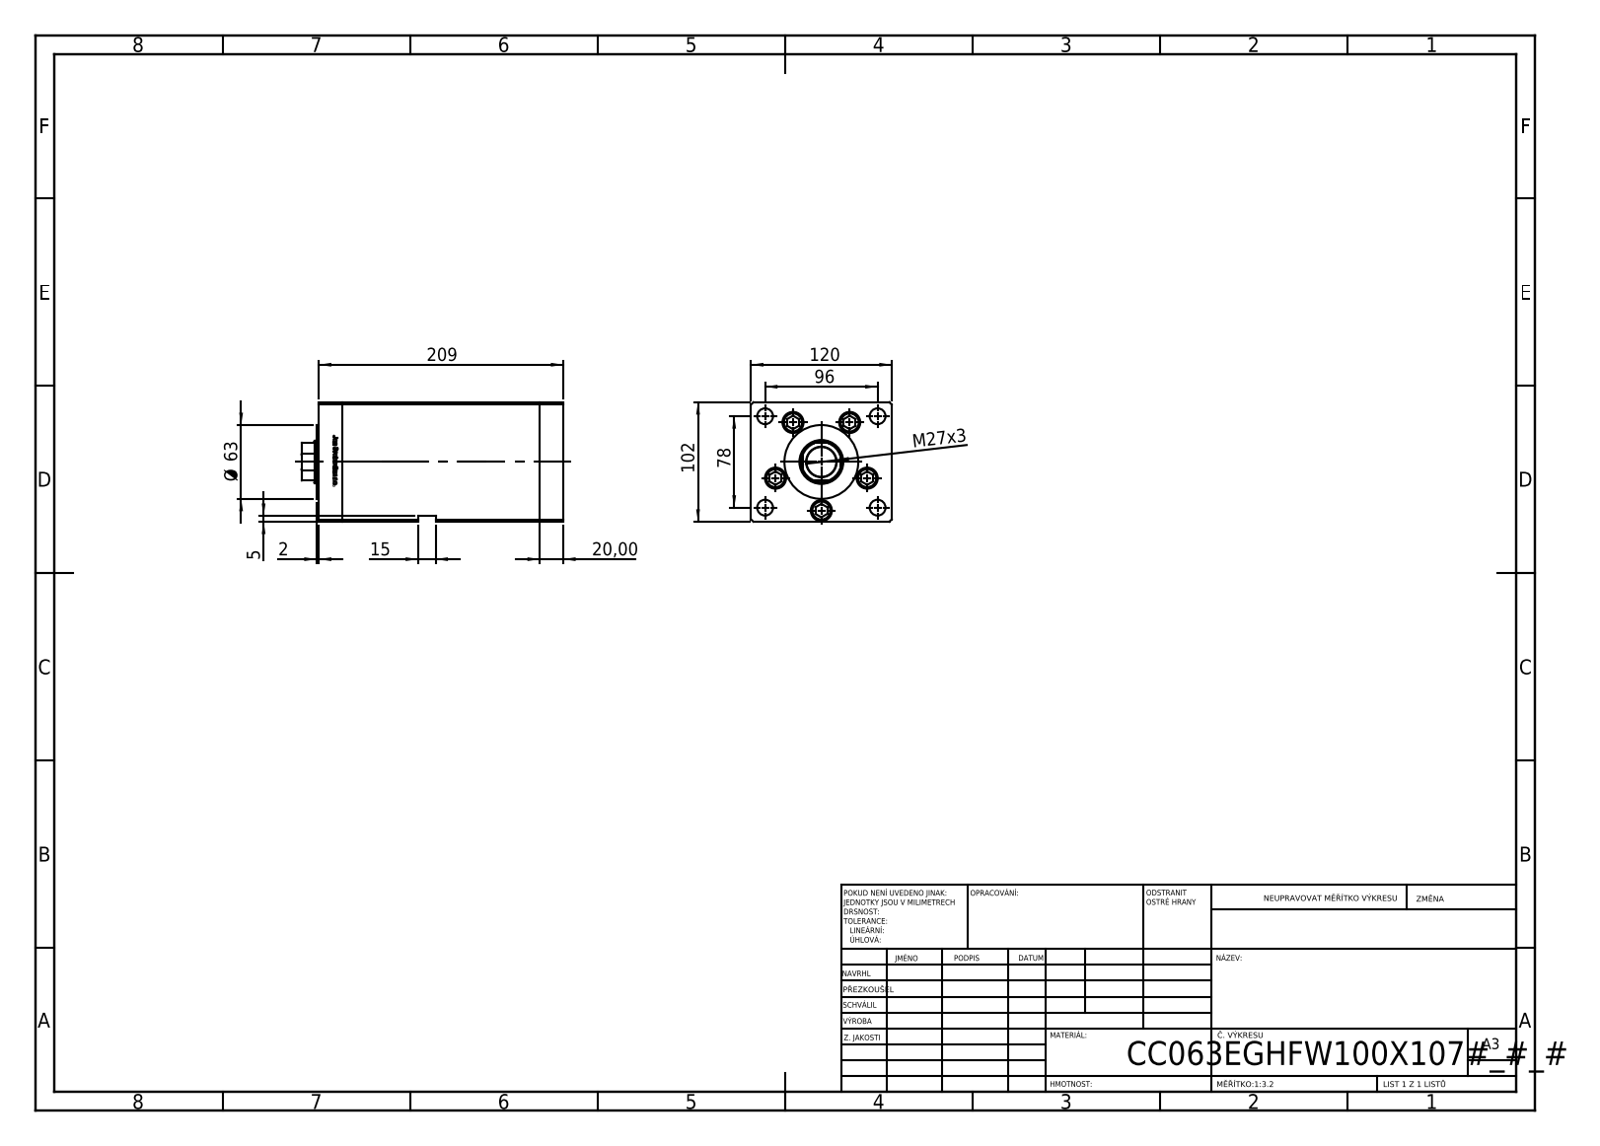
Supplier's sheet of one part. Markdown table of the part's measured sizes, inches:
| quantity | value |
| --- | --- |
| part name | ALLEN BOLT; V220C BACK_E; V220C_FRONT_E; V220C_VC_E (+1 more) |
| STEP written by | SolidWorks 2019 (CONFIG_CONTROL_DESIGN) |
| units | inches |
| bodies | 14 solids, 1214 faces (475 planar, 165 cylindrical, 574 other) |
| overall size | 8.799 × 4.724 × 4.016 |
| volume | 132.5 in³ |
| surface area | 449.3 in² |
| round holes (diameter × count) | 0.531 × 9, 0.709 × 5, 0.492 × 4, 0.728 × 4, 0.079 × 2, 0.518 × 2, 1.004 × 1, 1.417 × 1, 1.476 × 1 |
| round bosses / shafts (diameter × count) | 0.669 × 5, 0.315 × 5, 2.48 × 1 |
| partial cylindrical surfaces (radius × count) | 0.037 × 2, 0.689 × 1 |
| main face-to-face distances | 4.724, 0.787, 4.016, 6.634, 7.421, 1.348, 8.209, 0.561, 6.073, 6.86 |
| hole center spacings | 1.634, 2.435, 0.96, 1.051, 1.887, 1.893, 1.962, 2.109 |
